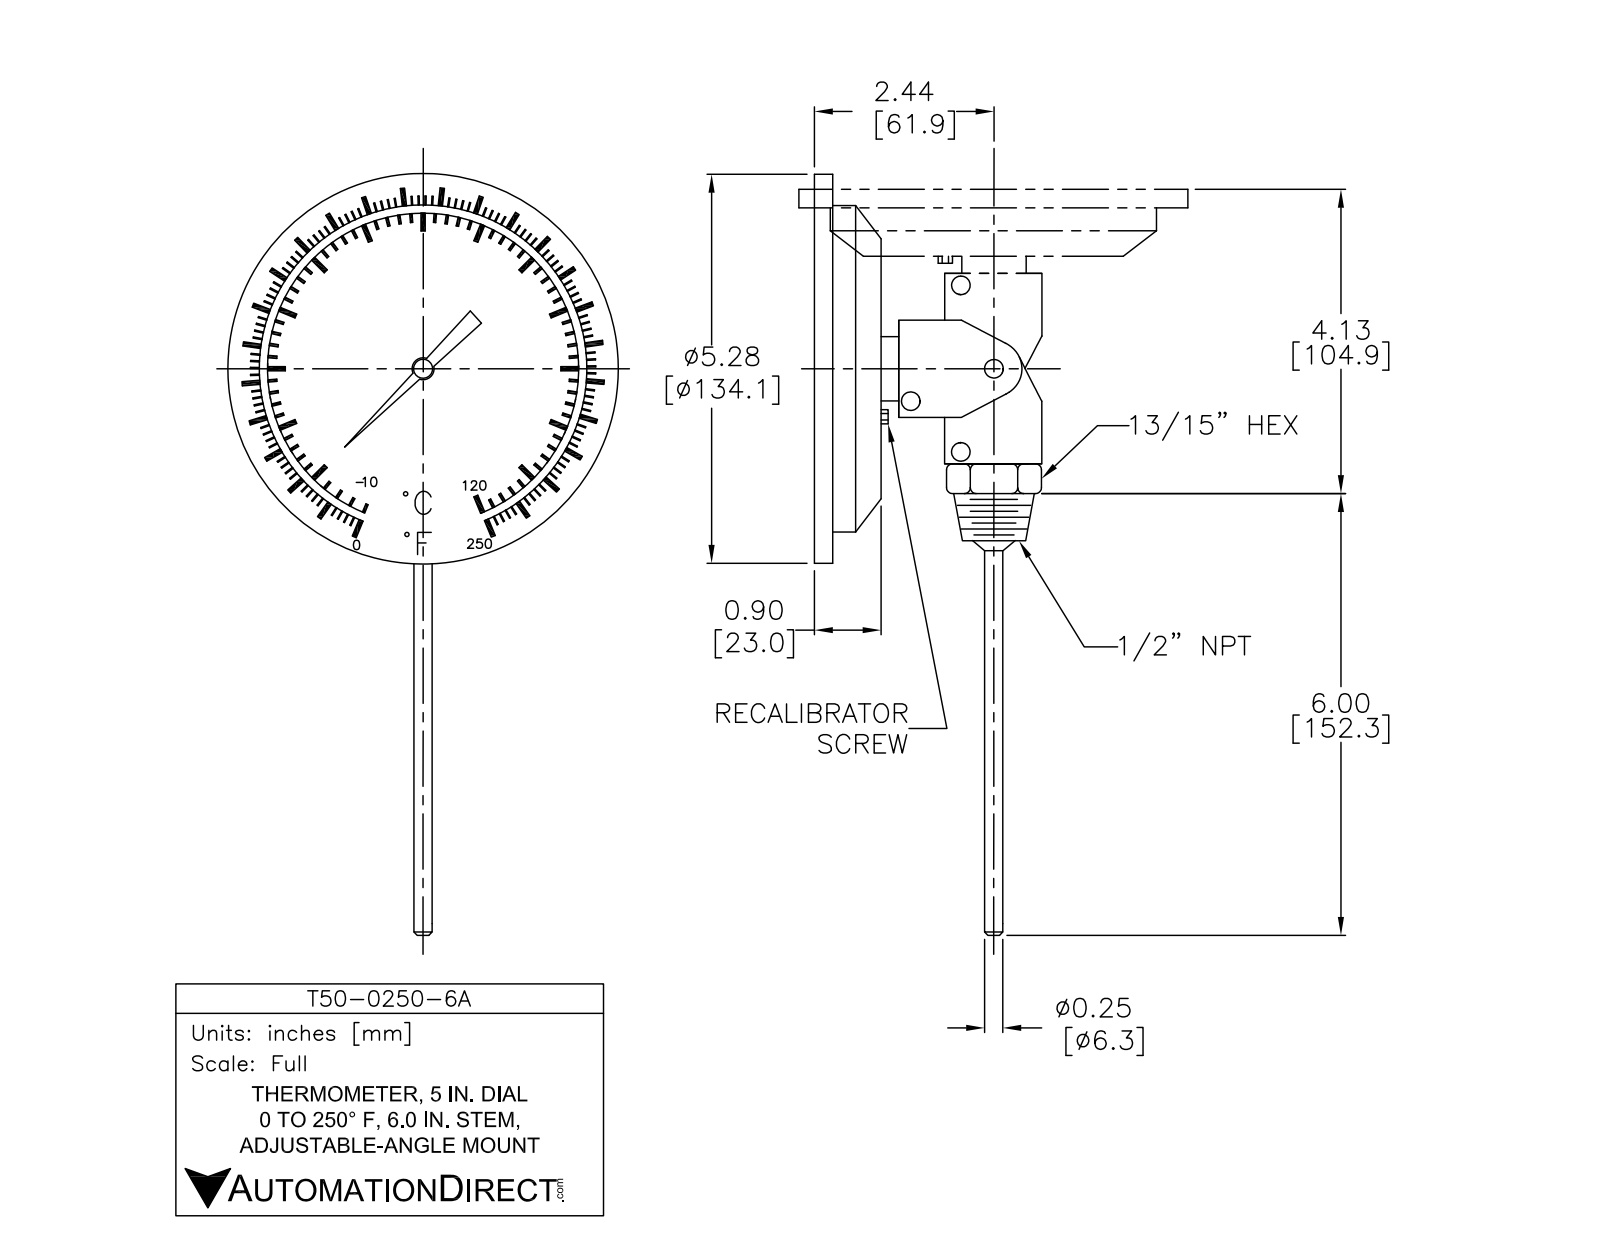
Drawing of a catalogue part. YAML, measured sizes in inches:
part_name: "T50-0250-6A"
step_written_by: "SolidWorks 2021 (AUTOMOTIVE_DESIGN)"
units: inches
bodies: {solids: 1, faces: 467, planar: 268, cylindrical: 45, other: 154}
overall_size: [9.96, 5.28, 5.28]
volume: 10.23
surface_area: 98.37
round_holes:
  - {diameter: 3.424, count: 1}
  - {diameter: 3.7, count: 1}
  - {diameter: 4.76, count: 1}
  - {diameter: 4.836, count: 1}
round_bosses_or_shafts:
  - {diameter: 0.305, count: 4}
  - {diameter: 0.145, count: 2}
  - {diameter: 5.28, count: 1}
  - {diameter: 4.97, count: 1}
  - {diameter: 3.73, count: 1}
  - {diameter: 3.454, count: 1}
  - {diameter: 0.85, count: 1}
  - {diameter: 0.821, count: 1}
partial_cylinders:
  - {radius: 0.06, count: 10}
  - {radius: 0.04, count: 4}
  - {radius: 0.17, count: 1}
  - {radius: 0.336, count: 1}
  - {radius: 0.336, count: 1}
  - {radius: 0.342, count: 1}
  - {radius: 0.4, count: 1}
face_to_face_distances: [0.353, 0.074, 0.055, 0.427, 1.19, 0.815, 0.462, 0.388, 1.245, 2.435]
